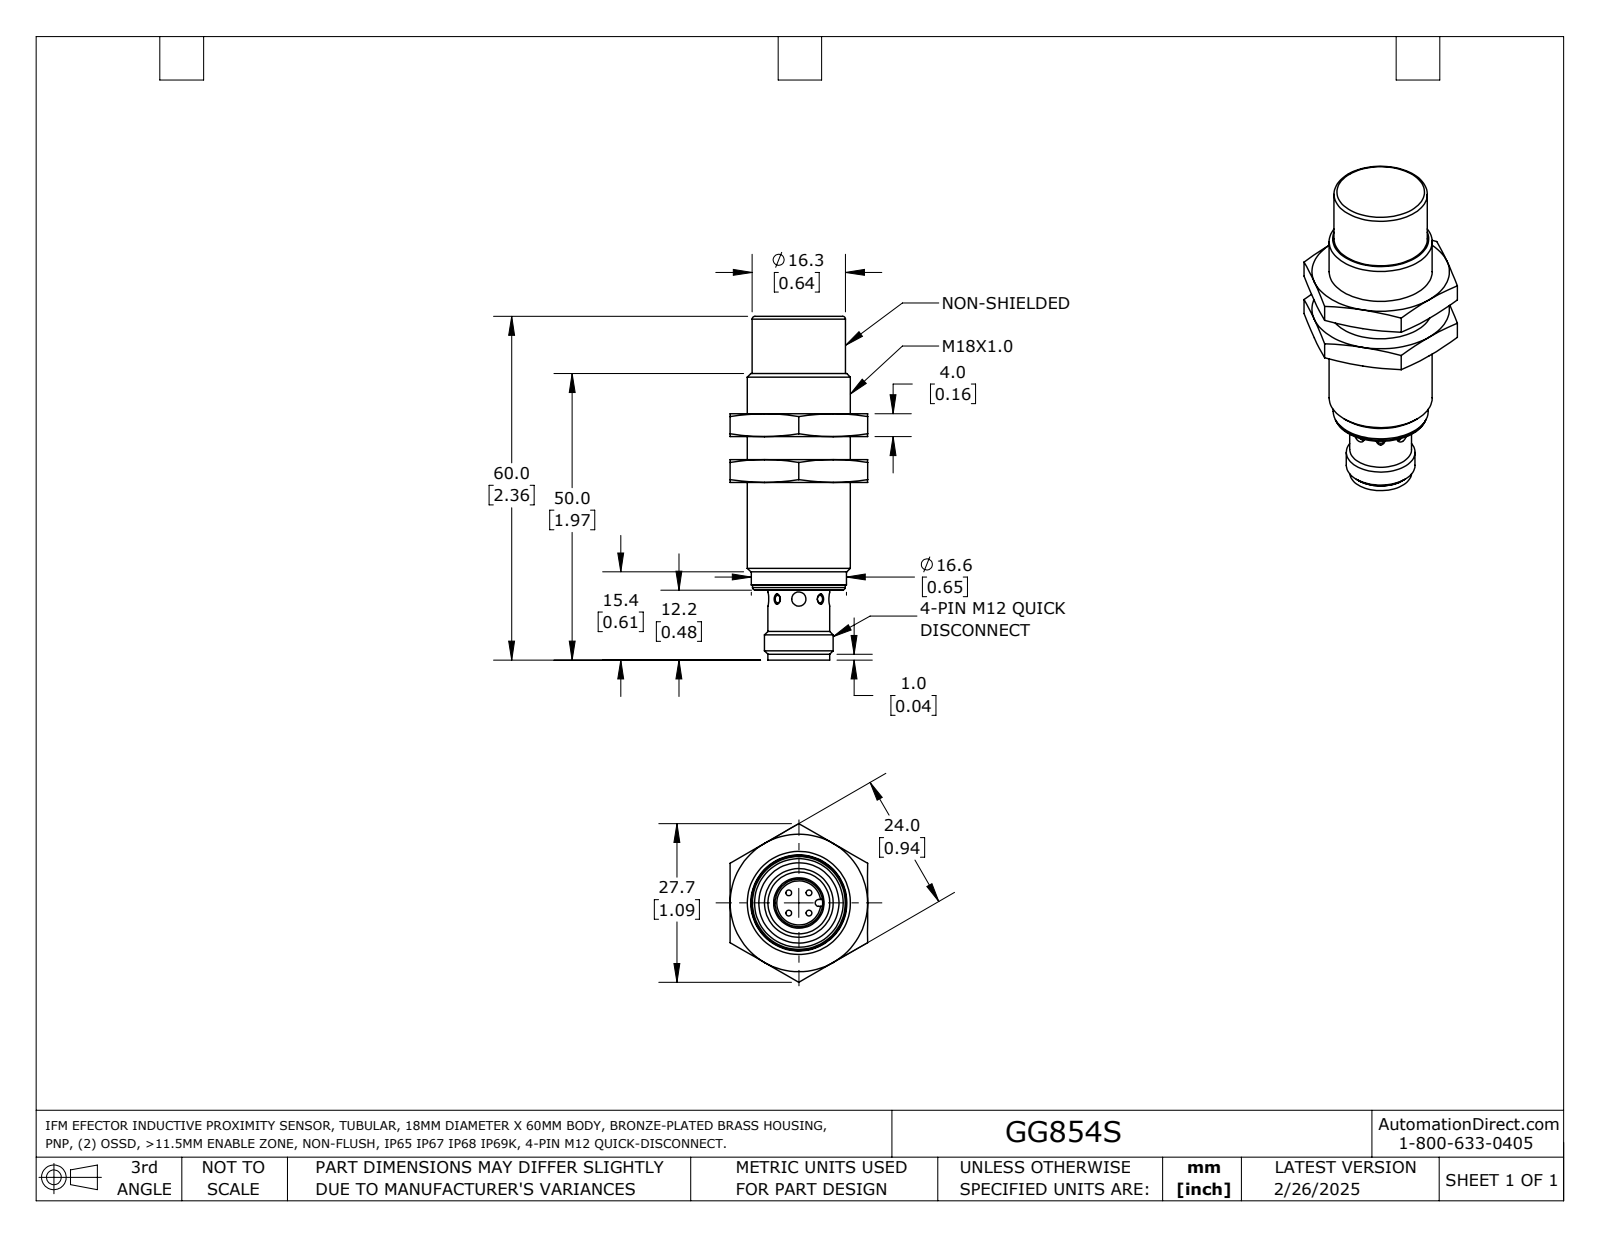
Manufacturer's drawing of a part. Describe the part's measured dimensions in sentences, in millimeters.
The part is named "GG854S". Its 3-D file was written by "SolidWorks 2024 (AUTOMOTIVE_DESIGN)". It is 3 solids with 92 faces: 27 planar, 19 cylindrical and 46 other. Overall it measures 60 by 27.71 by 24 millimeters. Its volume is 14 383 cubic millimeters and its surface area 5 862 square millimeters. Round holes: 2 of diameter 2.5, 1 of diameter 8.3, 1 of diameter 16.92. Round bosses or shafts: 1 of diameter 18, 1 of diameter 16.6, 1 of diameter 16.3, 1 of diameter 16.2, 1 of diameter 12, 1 of diameter 10.8. Partial cylindrical surfaces (rounded edges, fillets, slot ends): 1 of radius 0.6, 1 of radius 4.7. The main face-to-face distances are 4, 8, 23.99, 12, 29, 25, 21, 17, 24, 18.8.
